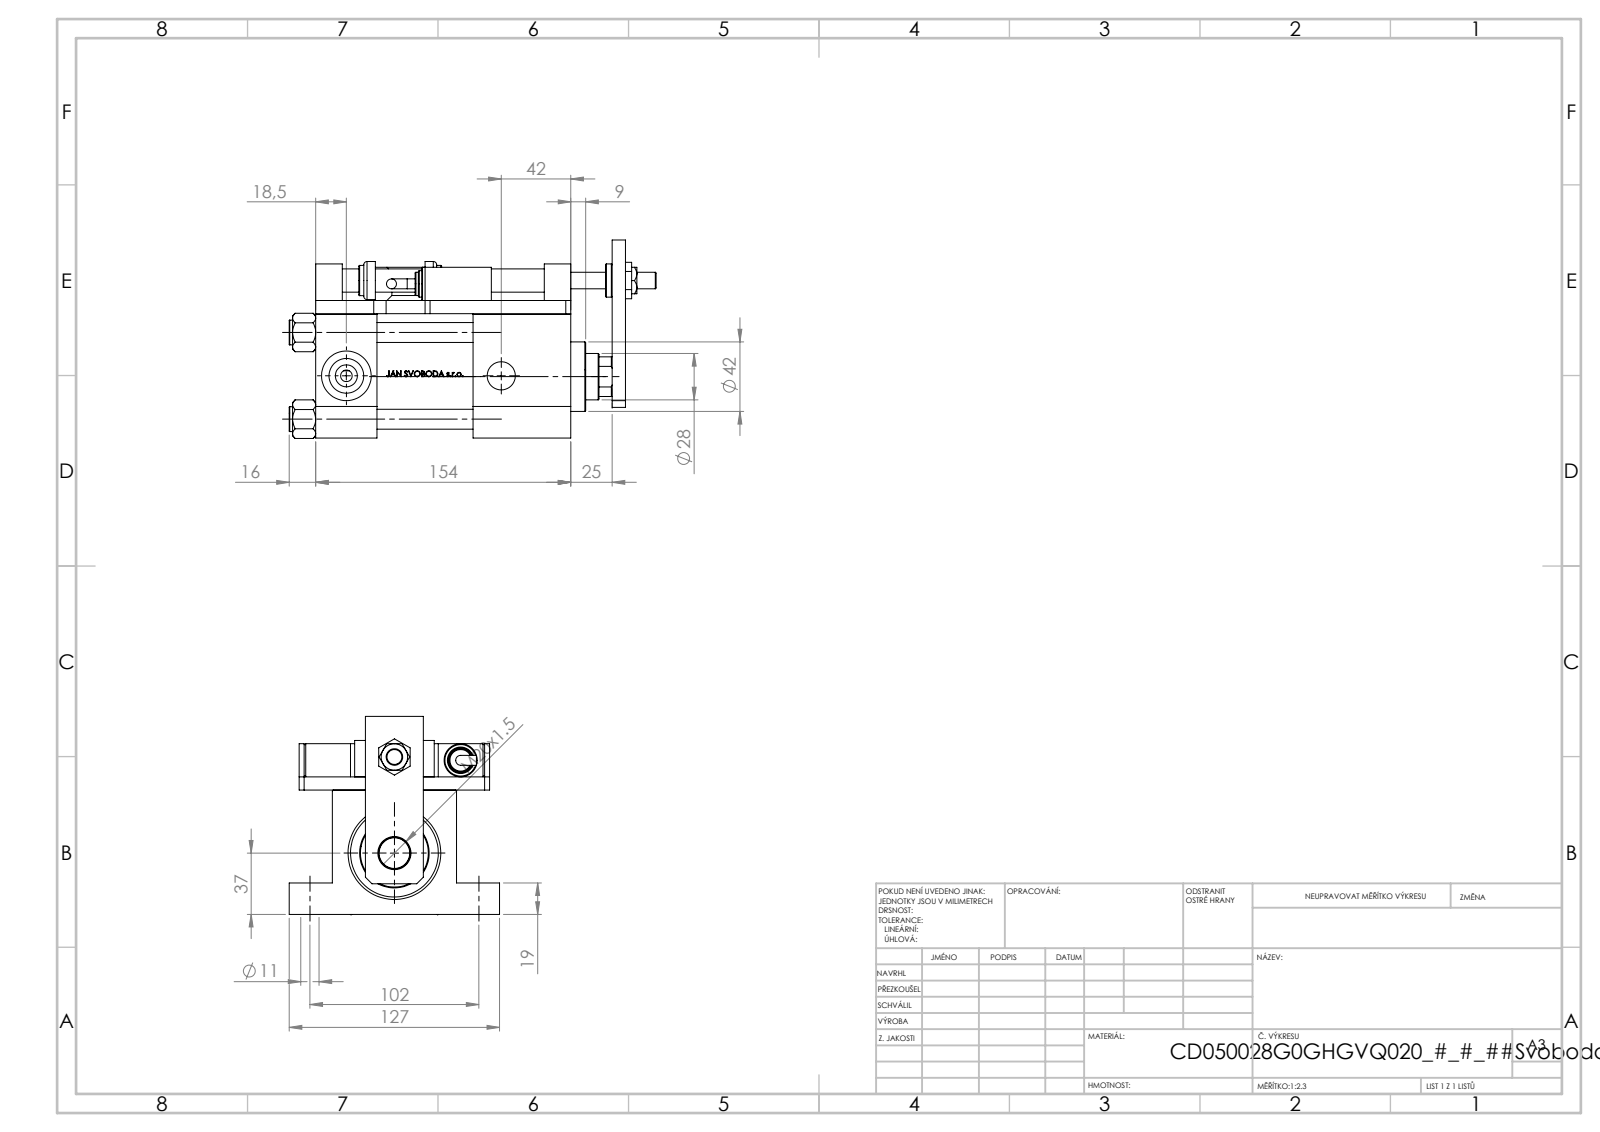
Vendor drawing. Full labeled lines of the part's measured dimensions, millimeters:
Part name (STEP PRODUCT): V215CD_SWITCH_Q_NUT; V215CD_SWITCH_Q_SWITCH; V215CD_SWITCH_Q_PODLOZKA_BACK; V215CD_G_TYCINKA (+7 more)
STEP written by: SolidWorks 2019 (CONFIG_CONTROL_DESIGN)
Units: millimetres
Bodies: 24 solids, 1315 faces (552 planar, 192 cylindrical, 571 other)
Overall size (bounding box): 221.5 × 127 × 119.77
Volume: 1 025 000 mm³ · Surface area: 246 056 mm²
Round holes (diameter × count): ⌀8.5 ×4, ⌀11 ×4, ⌀12 ×4, ⌀13.5 ×4, ⌀7 ×2, ⌀14 ×2, ⌀20.96 ×2, ⌀10 ×1, ⌀17 ×1, ⌀18.5 ×1, ⌀20 ×1, ⌀28 ×1
Round bosses / shafts (diameter × count): ⌀15 ×4, ⌀20 ×3, ⌀16 ×2, ⌀14 ×2, ⌀6 ×2, ⌀56 ×1, ⌀42 ×1, ⌀23 ×1
Partial cylindrical surfaces — rounded edges, fillets, slot ends (radius × count): R7.5 ×4, R13.5 ×1
Main face-to-face distances: 8, 75, 83, 20, 37, 95, 154, 117, 84, 59
Hole centre spacings: 40.82, 52.3, 32, 35.36, 36.63, 37.34, 40.44, 67.19
